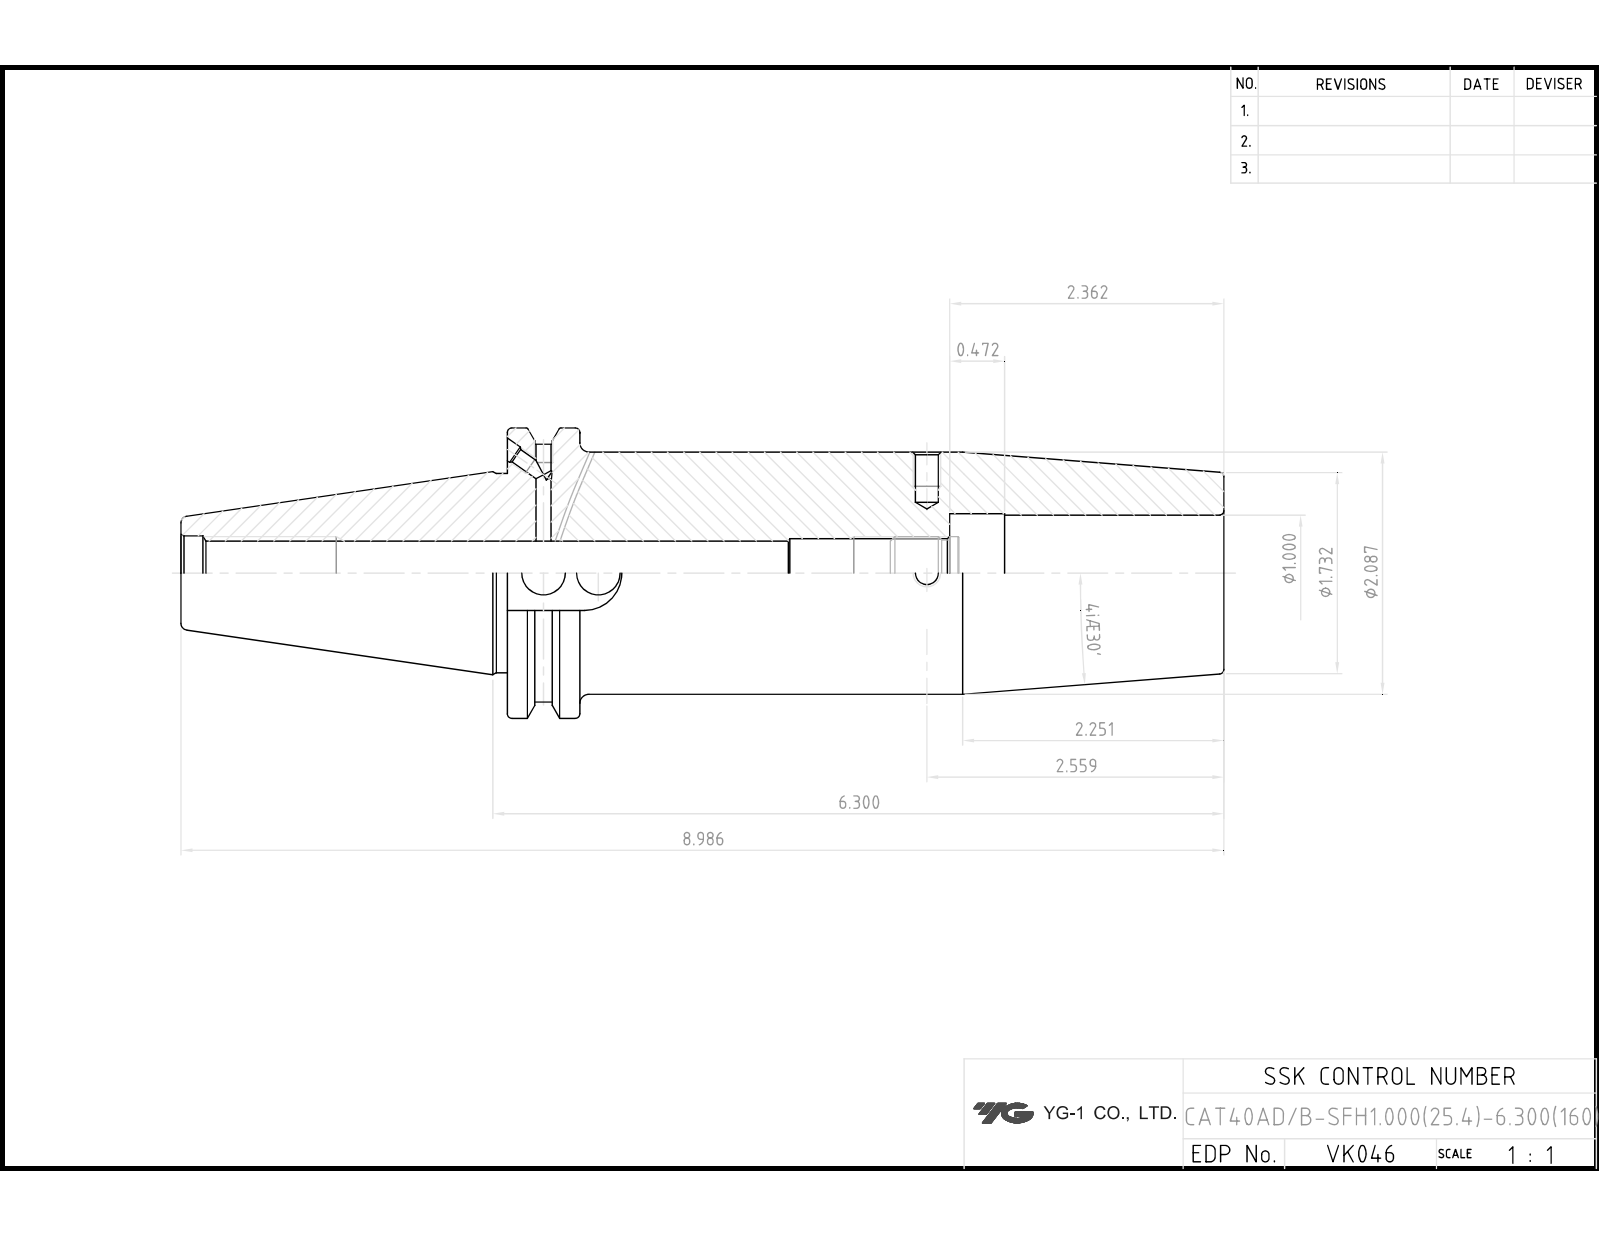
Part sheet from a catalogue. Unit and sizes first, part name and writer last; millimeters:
Units: millimetres
Overall size (bounding box): 228.25 × 63.5 × 61.09
Round holes (diameter × count): ⌀3.24 ×4, ⌀4 ×2, ⌀4.2 ×2, ⌀9.53 ×1, ⌀13 ×1, ⌀13.39 ×1, ⌀14.92 ×1, ⌀16.3 ×1, ⌀25.4 ×1, ⌀26.6 ×1
Round bosses / shafts (diameter × count): ⌀63.5 ×1, ⌀53 ×1, ⌀43.6 ×1
Partial cylindrical surfaces — rounded edges, fillets, slot ends (radius × count): R8.19 ×1, R28.15 ×1
Main face-to-face distances: 156.83, 96.83, 60, 15.88, 80.95, 140.95, 47.6, 16.38, 71.42, 87.3
Volume: 347 746 mm³ · Surface area: 51 118 mm²
Bodies: 1 solid, 87 faces (34 planar, 31 cylindrical, 22 other)
Part name (STEP PRODUCT): LO-CAT40ADB-SFH25.4-160
STEP written by: Autodesk Inventor 2022 (AUTOMOTIVE_DESIGN)
